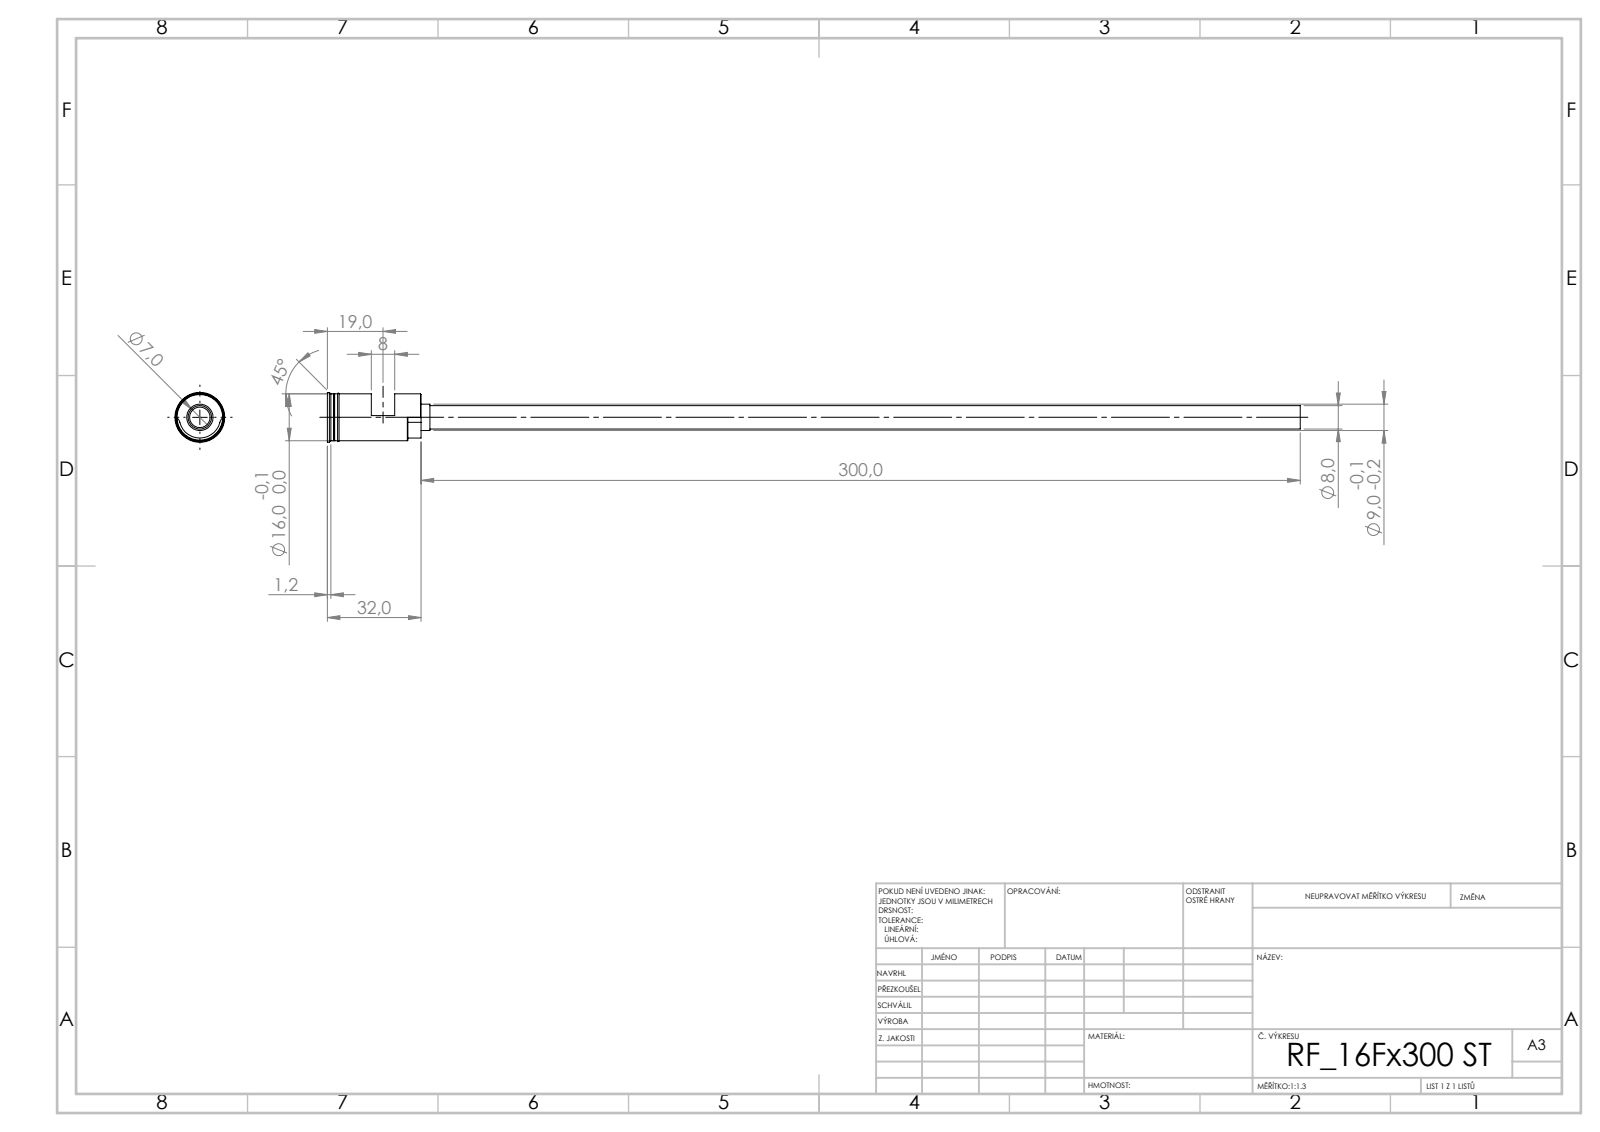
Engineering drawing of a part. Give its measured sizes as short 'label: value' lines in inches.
written by: SolidWorks 2019 (CONFIG_CONTROL_DESIGN)
unit: in
bodies: 1 solid, 55 faces (24 planar, 19 cylindrical, 12 other)
size: 13.071 × 0.669 × 0.669
volume: 0.514 in³; area: 25.75 in²
holes: 1× ⌀0.276
bosses: 1× ⌀0.669, 1× ⌀0.63, 1× ⌀0.622, 1× ⌀0.354, 1× ⌀0.315
rounds: 2× R0.118, 1× R0.278
face distances: 0.512, 0.669, 1.181, 0.079, 1.26, 0.591, 0.354, 0.315, 0.827, 0.906
